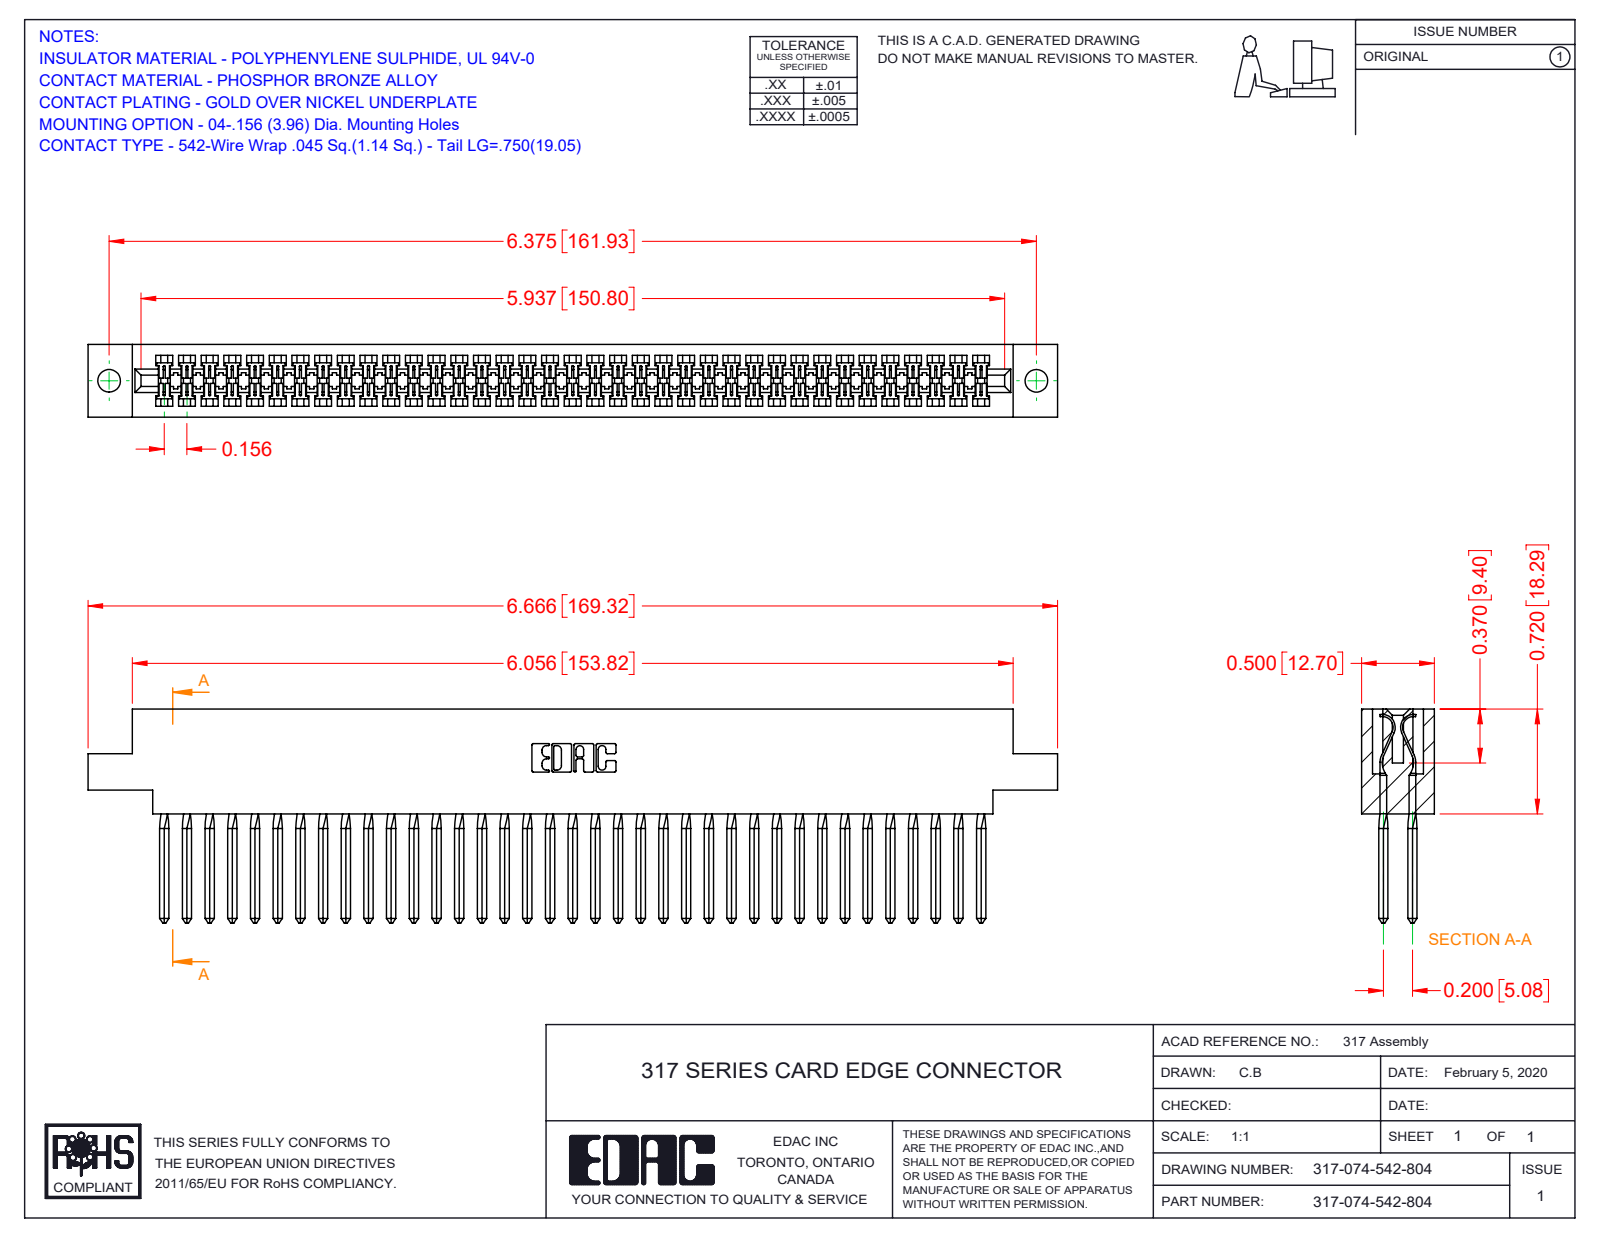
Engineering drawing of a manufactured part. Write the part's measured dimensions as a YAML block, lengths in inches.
part_name: "317 Part_.156 Dia - TH; 317-290-003_542; 317-074-542-804"
step_written_by: "SolidWorks 2016 (CONFIG_CONTROL_DESIGN)"
units: inches
bodies: {solids: 75, faces: 4320, planar: 3462, cylindrical: 562, other: 296}
overall_size: [6.666, 1.47, 0.5]
volume: 1.677
surface_area: 58.7
round_holes:
  - {diameter: 0.156, count: 2}
partial_cylinders:
  - {radius: 0.006, count: 148}
  - {radius: 0.01, count: 22}
  - {radius: 0.007, count: 6}
  - {radius: 0.031, count: 6}
  - {radius: 0.026, count: 3}
  - {radius: 0.074, count: 2}
  - {radius: 0.089, count: 2}
  - {radius: 0.1, count: 2}
face_to_face_distances: [0.5, 0.075, 0.425, 0.35, 0.2, 0.046, 0.128, 0.372, 0.052, 0.297]
hole_center_spacings: [6.375]
